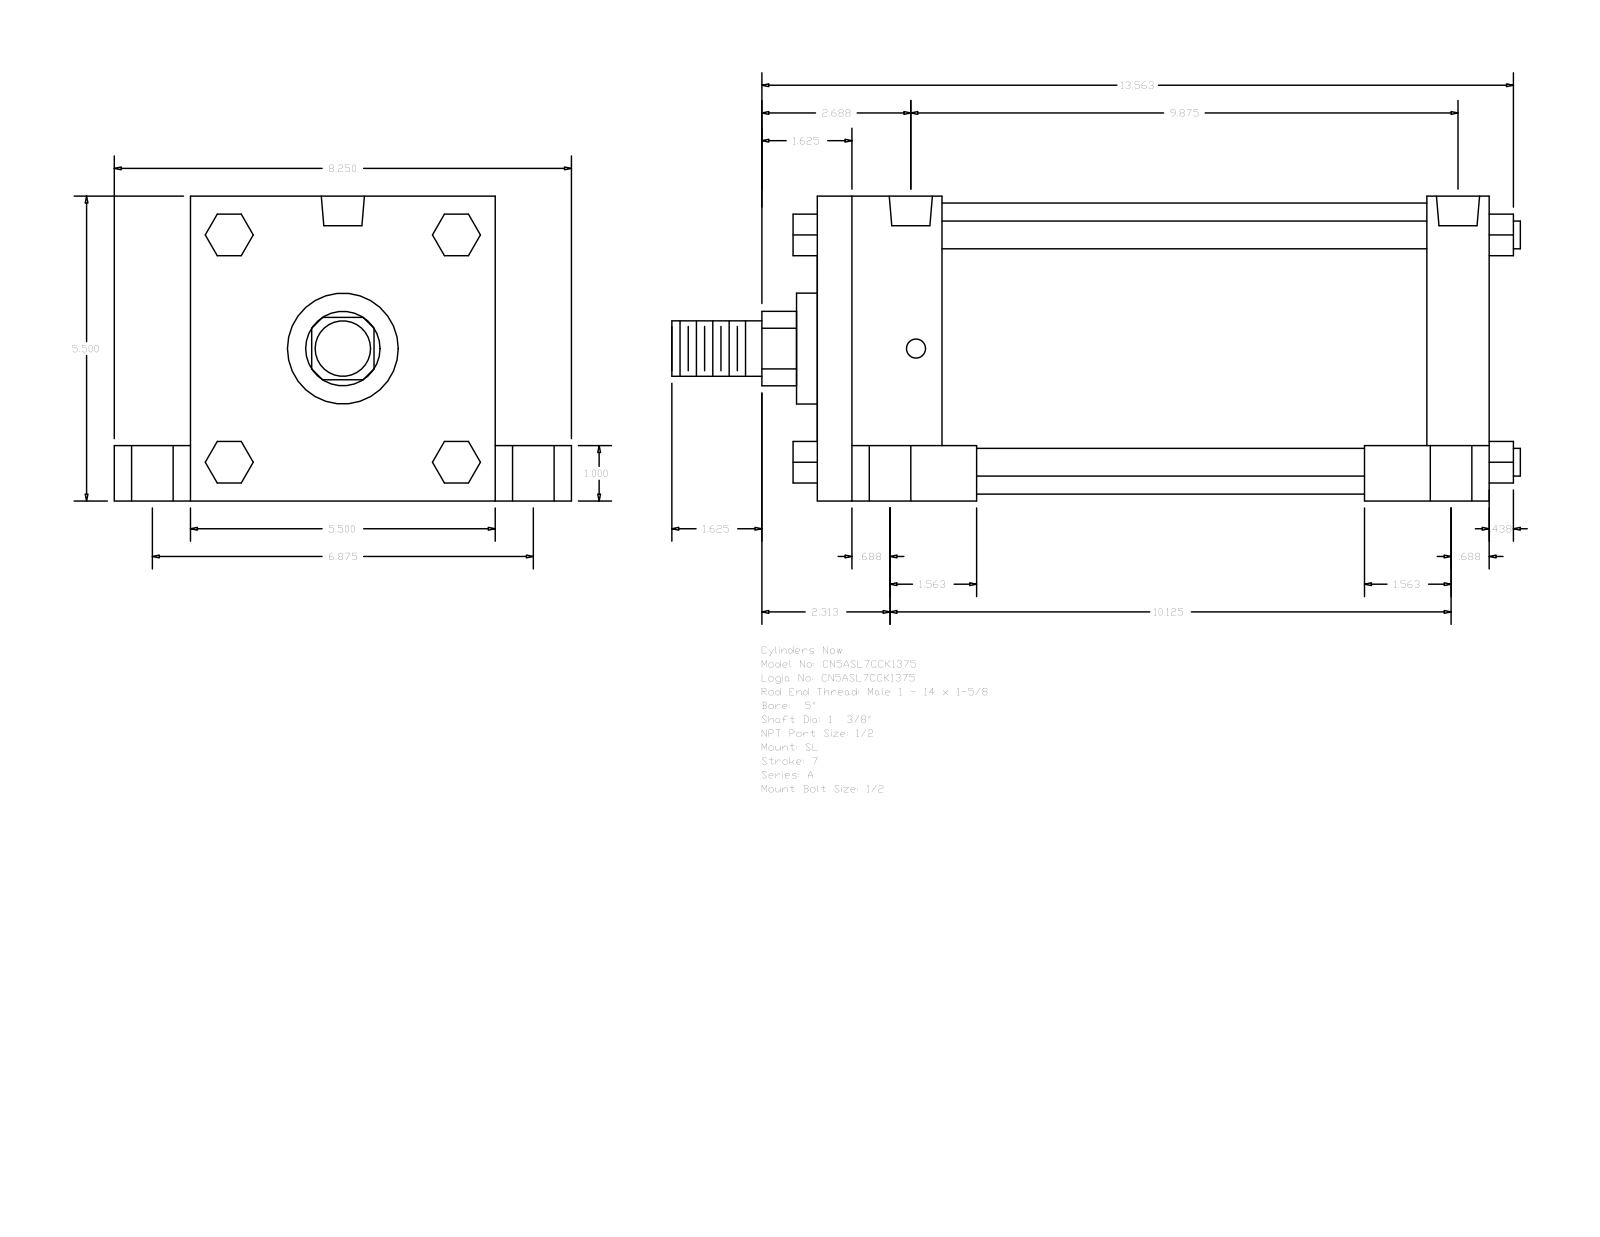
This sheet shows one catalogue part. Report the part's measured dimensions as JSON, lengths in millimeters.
{"part_name": "A_SL__0500_1.375", "step_written_by": "GSSL Pune (CONFIG_CONTROL_DESIGN)", "units": "millimeters", "bodies": {"solids": 0, "faces": 150, "planar": 114, "cylindrical": 36, "other": 0}, "overall_size": [388.94, 209.55, 139.7], "round_holes": [[8.73, 4], [19.05, 4], [25.4, 4], [19.77, 2]], "round_bosses_or_shafts": [[12.7, 4], [133.35, 1], [50.8, 1], [34.92, 1], [25.4, 1]], "partial_cylinders_radius": [[17.06, 1]], "face_to_face_distances": [139.7, 307.98, 57.15, 250.83, 25.4, 114.3, 34.93, 174.63, 28.58, 279.4], "hole_center_spacings": [2.39, 87.31, 87.37, 87.83, 88.12, 174.62, 246.05, 248.44]}
